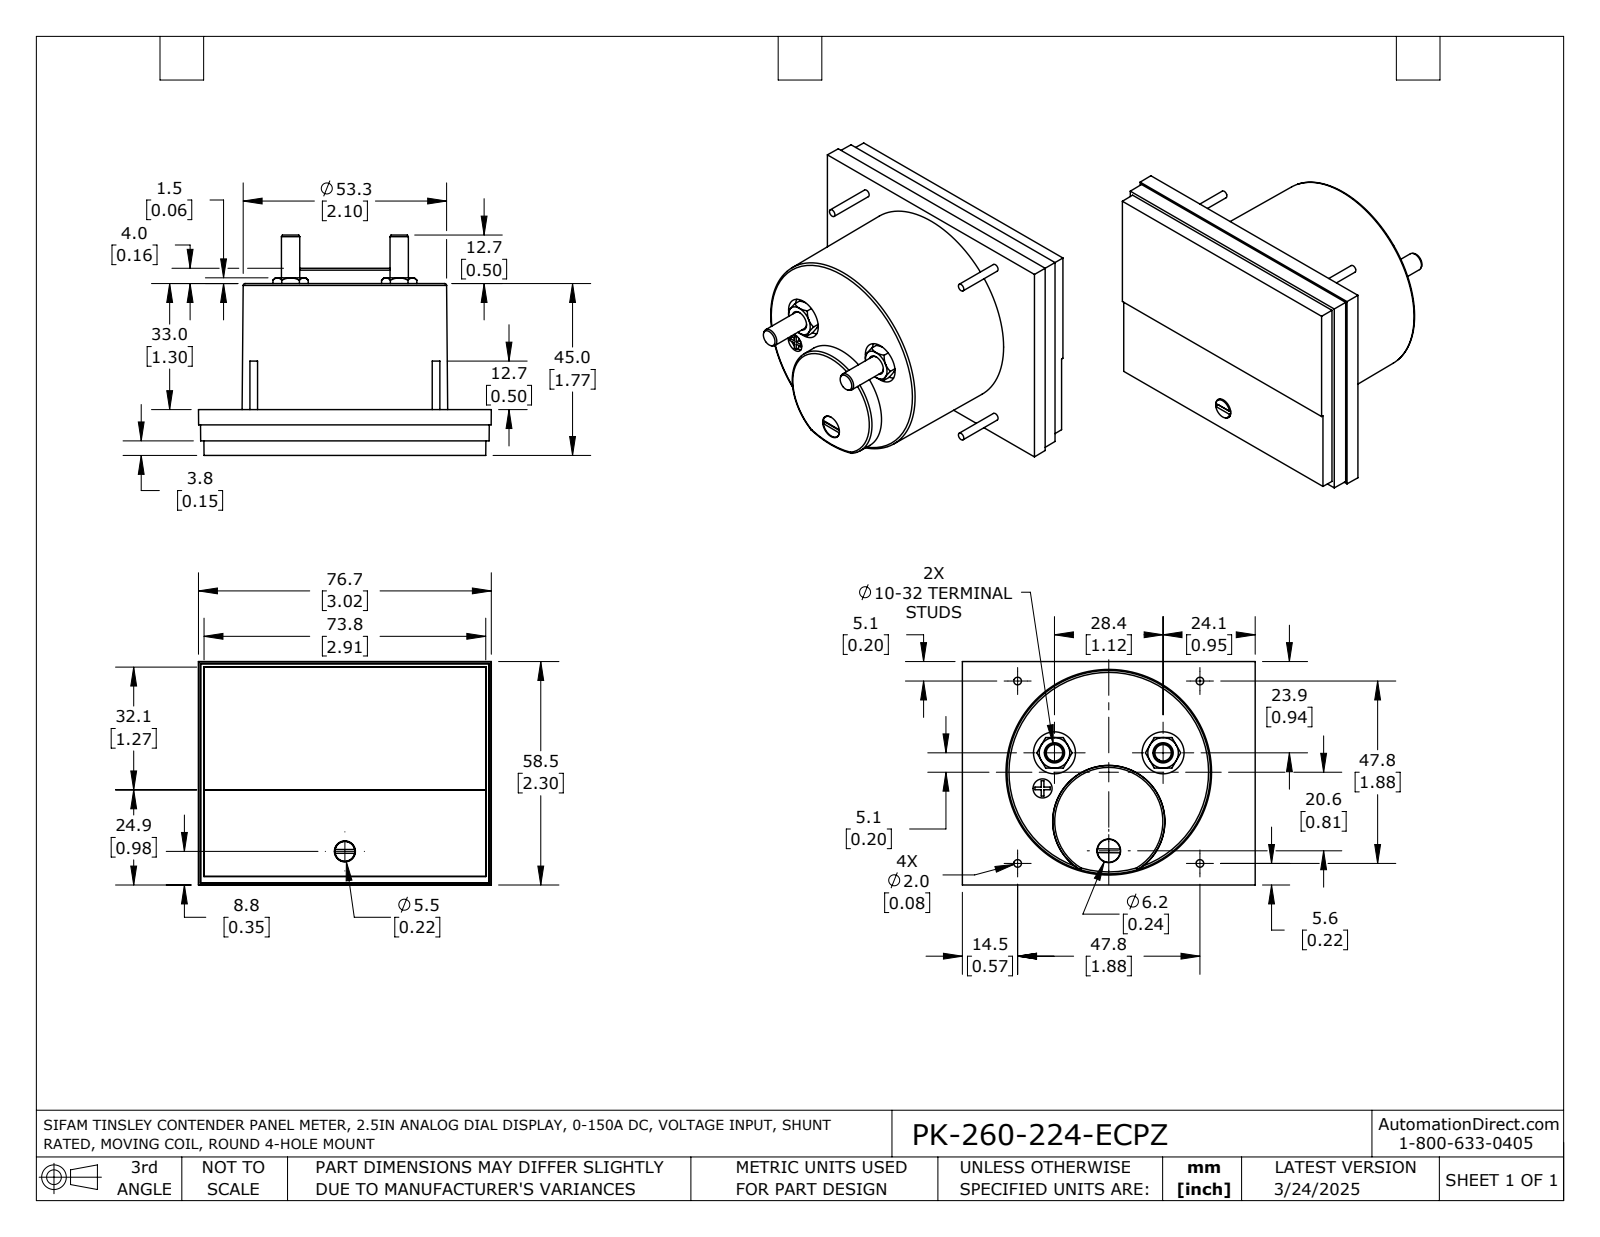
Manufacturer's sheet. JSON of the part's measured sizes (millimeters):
{"part_name": "PK-260-224-ECPZ", "step_written_by": "SolidWorks 2021 (AUTOMOTIVE_DESIGN)", "units": "millimeters", "bodies": {"solids": 1, "faces": 192, "planar": 95, "cylindrical": 37, "other": 60}, "overall_size": [76.7, 58.5, 57.7], "volume_mm3": 125500, "surface_area_mm2": 23580, "round_holes": [[5, 3], [11, 2], [5.3, 1], [5.5, 1], [6.2, 1]], "round_bosses_or_shafts": [[2, 4], [4.8, 2], [6, 1], [5.2, 1]], "partial_cylinders_radius": [[0.8, 1]], "face_to_face_distances": [0.5, 12, 3.3, 8.2, 3.8, 11.5, 1.4, 2, 10.1, 1.9], "hole_center_spacings": [29.3, 29.5, 9.8, 23.8, 23.9, 28.4, 32.9]}
